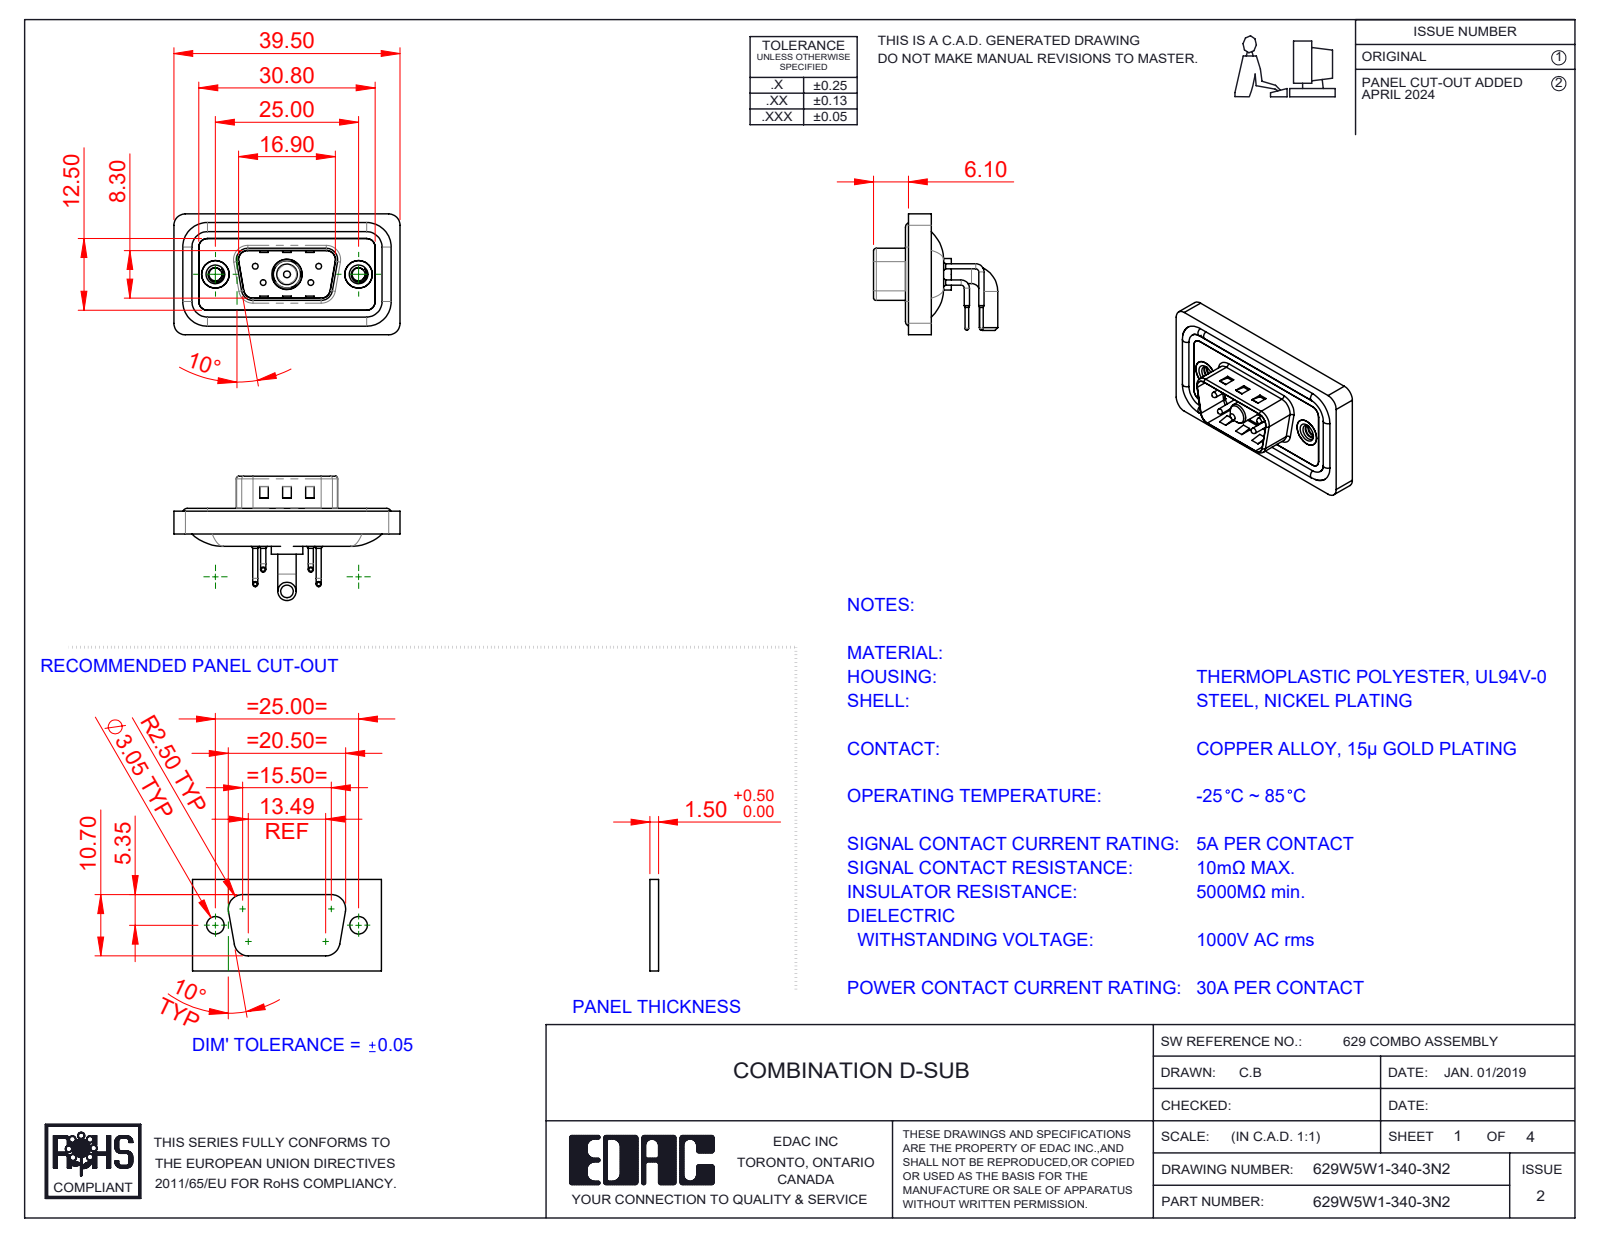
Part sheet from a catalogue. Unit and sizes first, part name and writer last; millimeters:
Units: millimetres
Overall size (bounding box): 39.5 × 21.7 × 21.1
Round holes (diameter × count): ⌀0.75 ×4, ⌀1.6 ×4, ⌀2 ×4, ⌀2.26 ×2, ⌀4 ×2, ⌀4.8 ×2, ⌀5 ×2, ⌀4.85 ×1, ⌀5.3 ×1
Round bosses / shafts (diameter × count): ⌀0.9 ×8, ⌀1.6 ×4, ⌀1.5 ×4, ⌀1 ×4, ⌀0.65 ×4, ⌀4.9 ×2, ⌀3.2 ×2, ⌀5.5 ×1
Partial cylindrical surfaces — rounded edges, fillets, slot ends (radius × count): R1.5 ×18, R2 ×18, R0.5 ×8, R1.6 ×8, R0.25 ×4, R0.6 ×4, R0.65 ×4, R0.9 ×4
Main face-to-face distances: 0.4, 2.9, 1.1, 0.8, 2.1, 2.5, 1.6, 3.1, 4.5, 1.5
Hole centre spacings: 3.16, 5.72, 7.1, 12.5, 18.1, 4.39, 4.4, 8.31
Volume: 4 515 mm³ · Surface area: 7 183 mm²
Bodies: 13 solids, 894 faces (411 planar, 345 cylindrical, 138 other)
Part name (STEP PRODUCT): 629Combo Shell Rear_09 Contacts; 629Combo Shell Front_09 Contacts; 629W5W1-340-3N2; 629Combo Contact Row 1 (+5 more)
STEP written by: SolidWorks 2023 (CONFIG_CONTROL_DESIGN)
